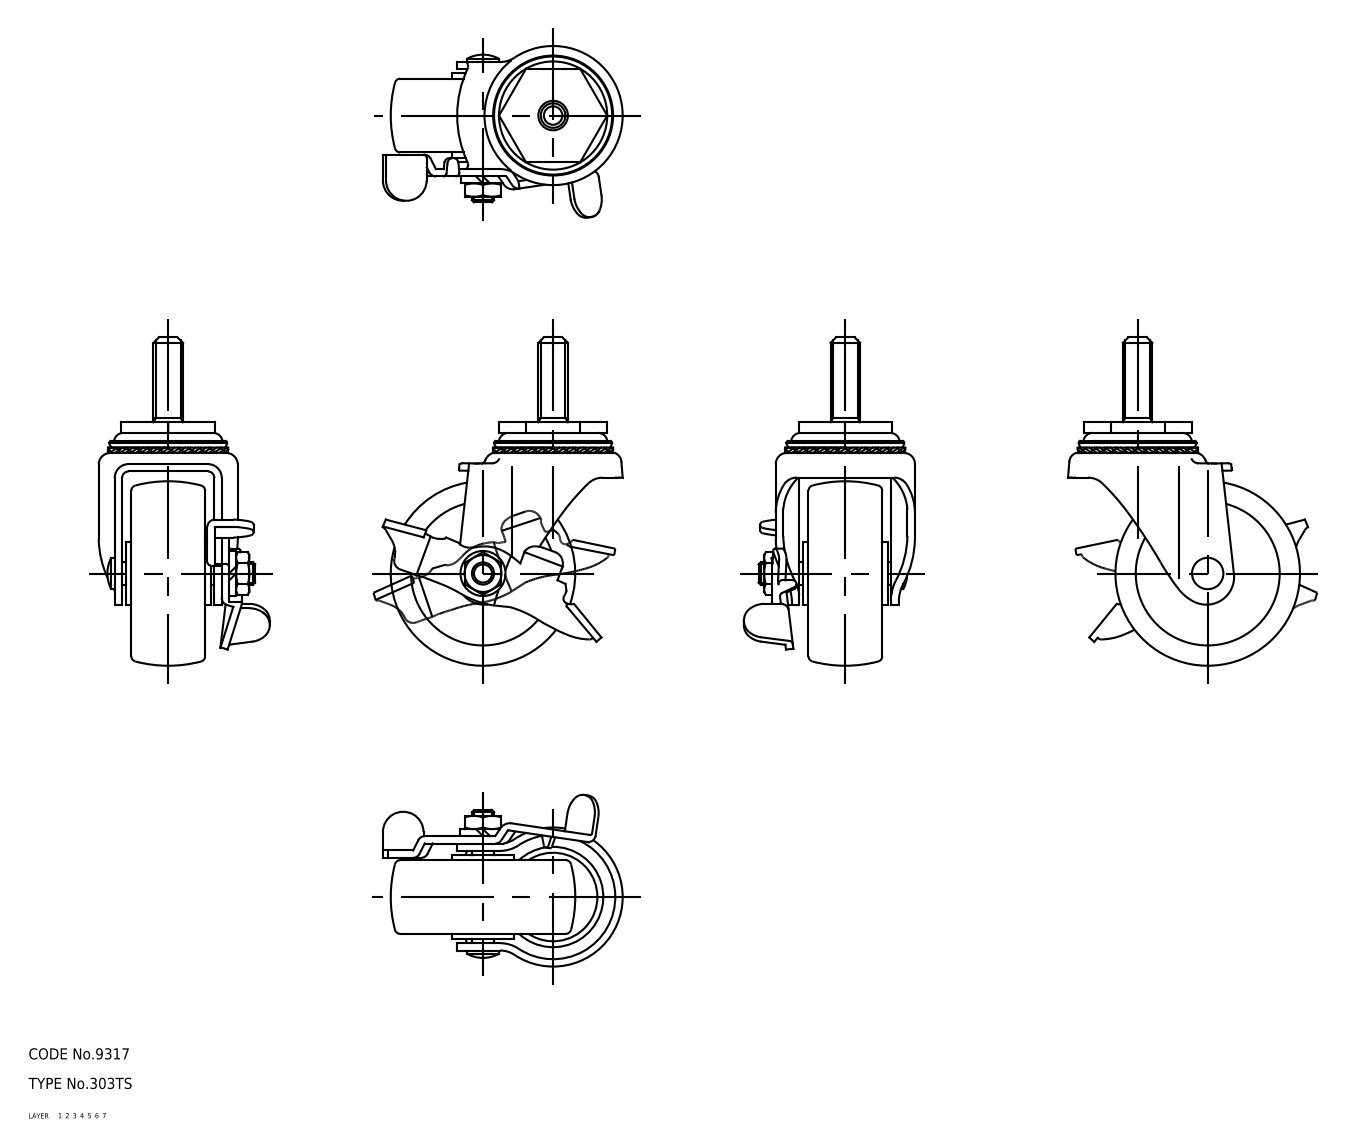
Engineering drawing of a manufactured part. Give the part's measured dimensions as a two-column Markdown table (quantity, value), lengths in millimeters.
| quantity | value |
| --- | --- |
| part name | 67127116; 67127129; 67127142; 67127155 (+1 more) |
| STEP written by | CADfix (AUTOMOTIVE_DESIGN) |
| units | millimeters |
| bodies | 6 solids, 290 faces (0 planar, 0 cylindrical, 290 other) |
| overall size | 89 × 65.04 × 46.41 |
| volume | 50 460 mm³ |
| surface area | 21 656 mm² |
